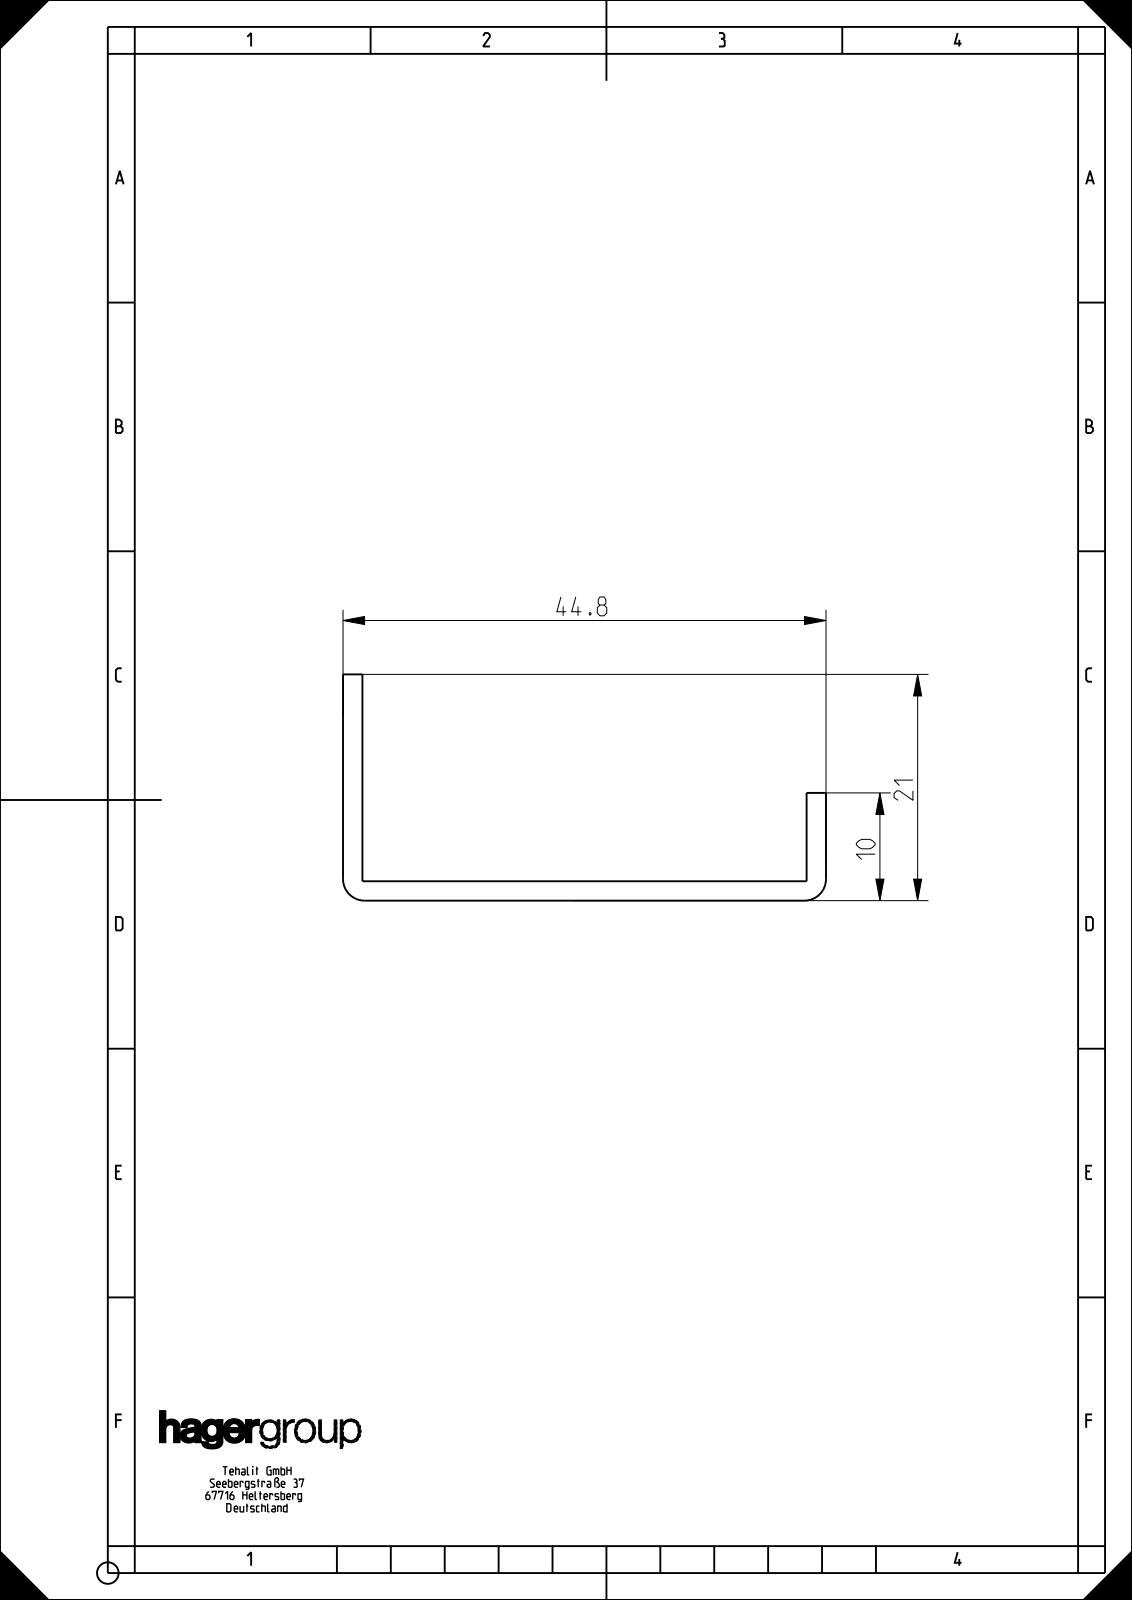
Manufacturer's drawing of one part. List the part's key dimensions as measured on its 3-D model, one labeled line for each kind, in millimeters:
Part name (STEP PRODUCT): BRN0452KUN
STEP written by: CREO PARAMETRIC BY PTC INC, 2022162 (AUTOMOTIVE_DESIGN)
Units: millimetres
Bodies: 1 solid, 12 faces (10 planar, 2 cylindrical, 0 other)
Overall size (bounding box): 2000 × 44.8 × 21
Volume: 256 486 mm³ · Surface area: 292 823 mm²
Partial cylindrical surfaces — rounded edges, fillets, slot ends (radius × count): R2 ×2
Main face-to-face distances: 1.8, 43, 41.2, 44.8, 21, 19.2, 10, 8.2, 11, 2000
